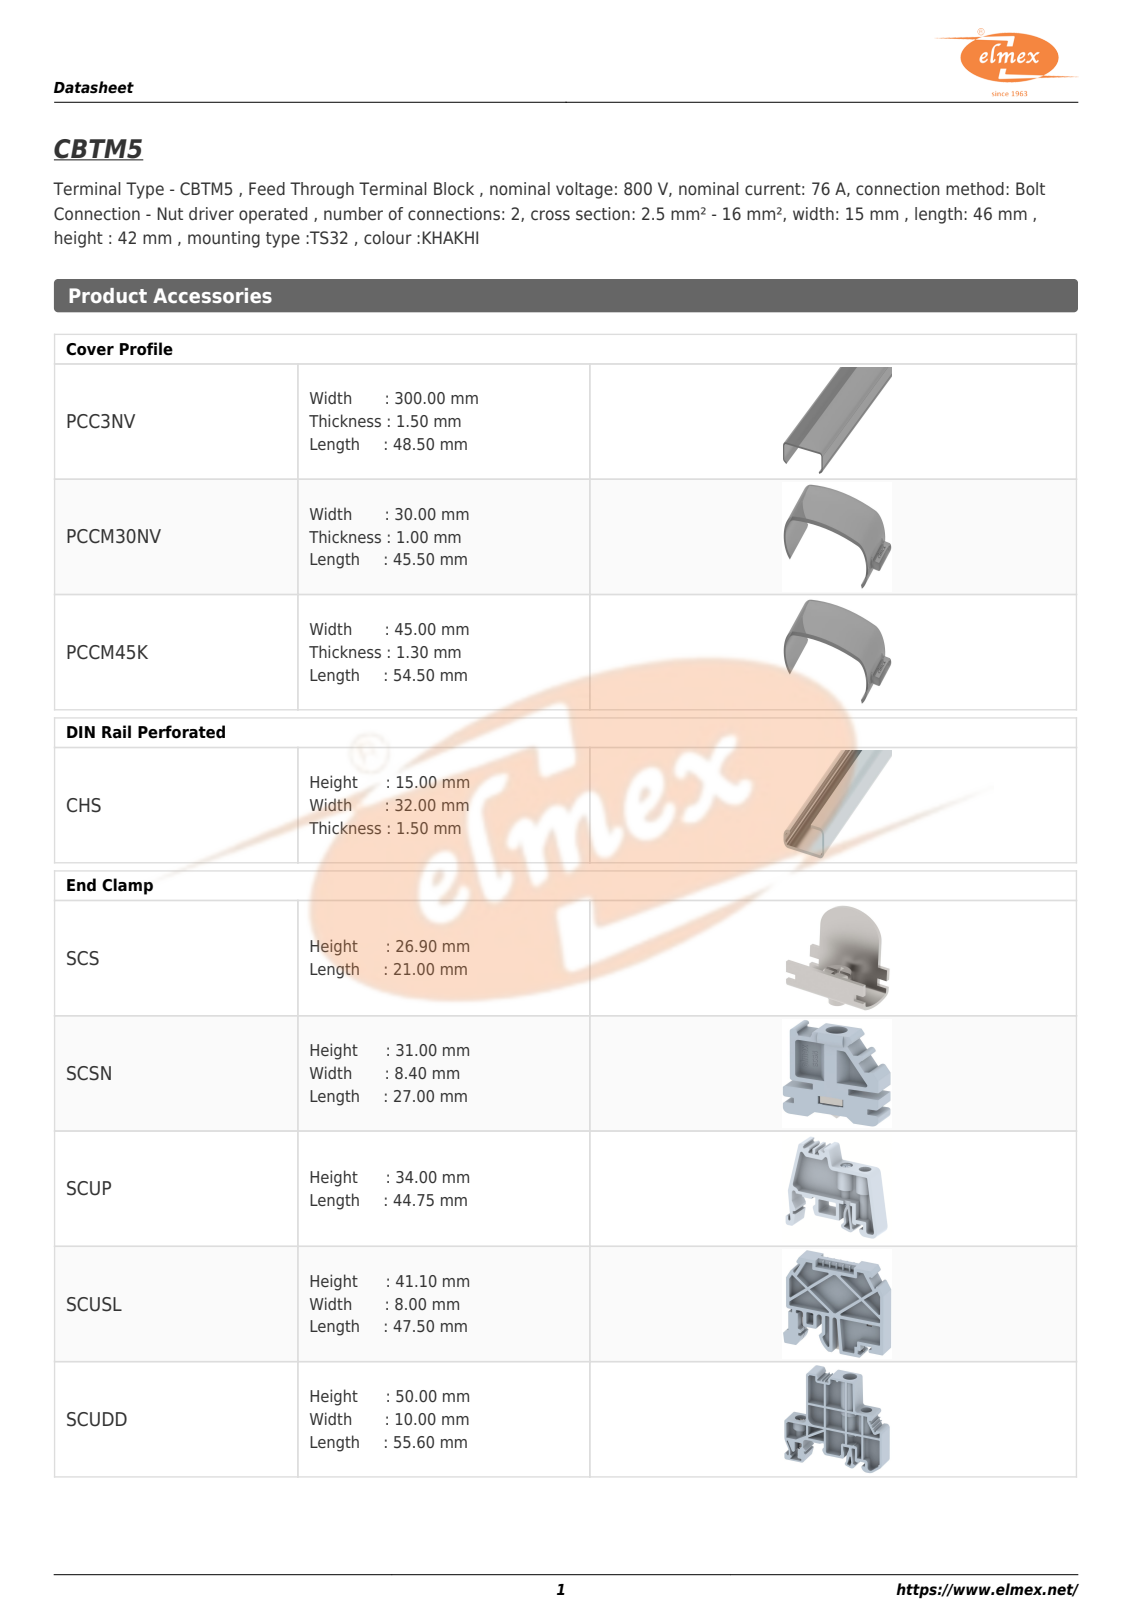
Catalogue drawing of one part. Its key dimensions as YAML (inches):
step_written_by: "ST-DEVELOPER v16 (AUTOMOTIVE_DESIGN)"
units: inches
bodies: {solids: 1, faces: 44, planar: 34, cylindrical: 10, other: 0}
overall_size: [1.969, 1.772, 0.591]
volume: 1.532
surface_area: 9.861
partial_cylinders:
  - {radius: 0.069, count: 4}
  - {radius: 0.059, count: 2}
  - {radius: 0.157, count: 2}
  - {radius: 0.065, count: 1}
  - {radius: 0.079, count: 1}
face_to_face_distances: [0.591, 1.969, 1.772, 1.642, 0.13, 1.181, 0.787, 0.709, 0.933, 1.063]
